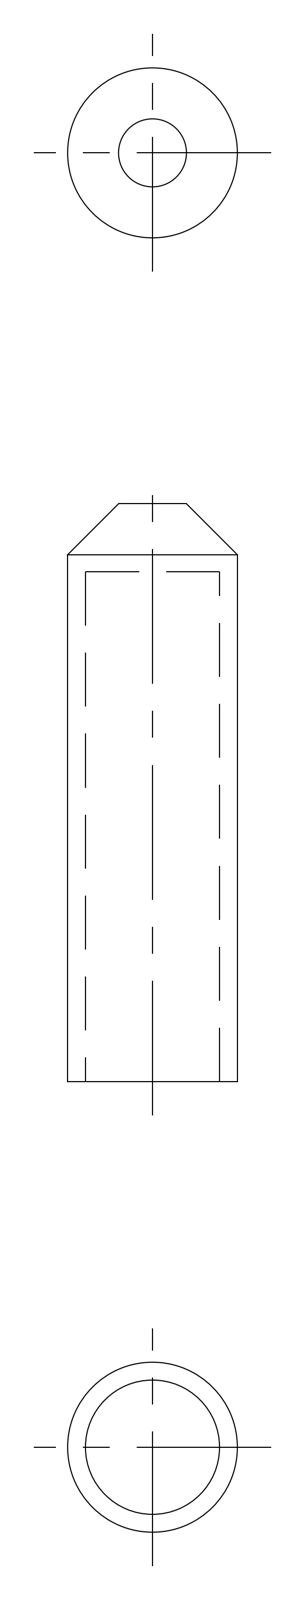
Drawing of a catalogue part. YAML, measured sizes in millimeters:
part_name: "cap; THA_324_1S"
step_written_by: "SolidWorks 2015 (AUTOMOTIVE_DESIGN)"
units: millimeters
bodies: {solids: 1, faces: 9, planar: 3, cylindrical: 4, other: 2}
overall_size: [34, 10, 10]
volume: 1087
surface_area: 1903
round_holes:
  - {diameter: 7.9, count: 1}
round_bosses_or_shafts:
  - {diameter: 10, count: 1}
face_to_face_distances: [30, 34, 4]
